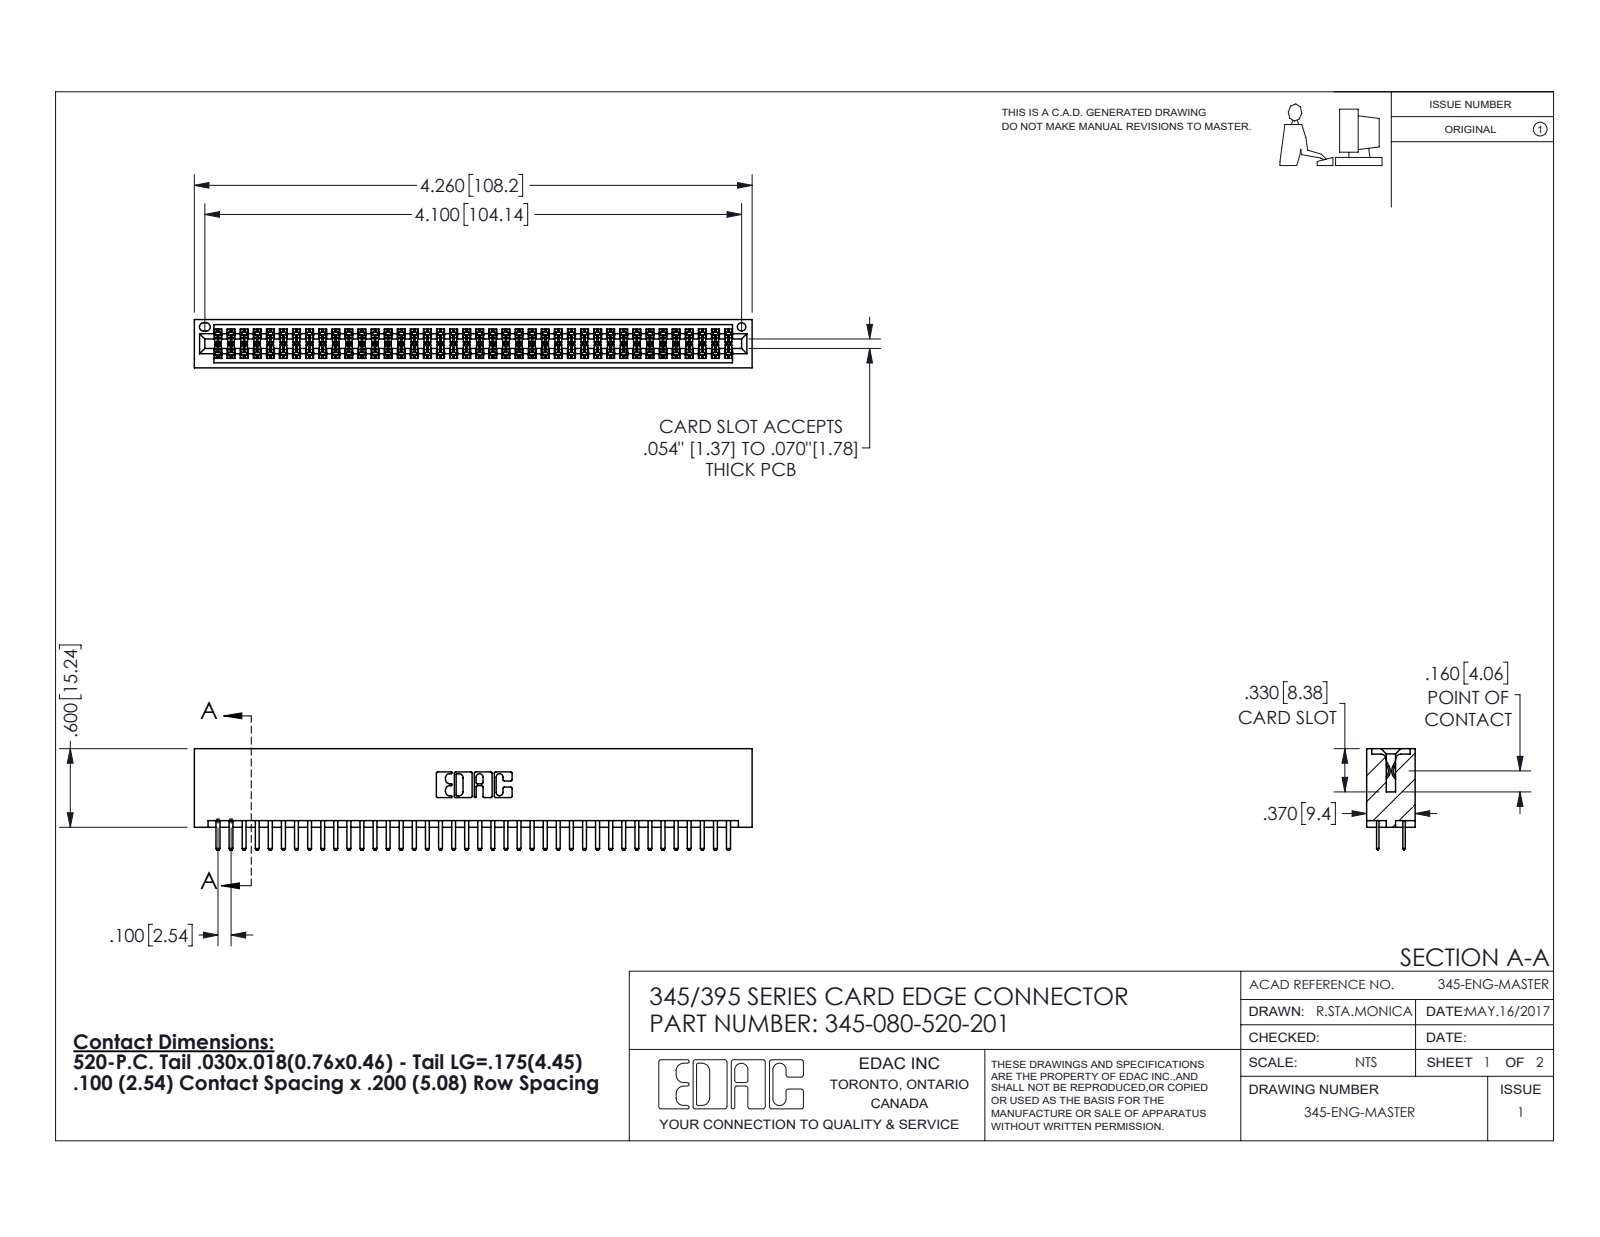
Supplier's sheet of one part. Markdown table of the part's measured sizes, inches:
| quantity | value |
| --- | --- |
| part name | 345-080-520-201; 345-292-001_345-293-120; 345 Part_No Mounting Lugs |
| STEP written by | SolidWorks 2016 (CONFIG_CONTROL_DESIGN) |
| units | inches |
| bodies | 81 solids, 4438 faces (2876 planar, 1562 cylindrical, 0 other) |
| overall size | 4.26 × 0.775 × 0.37 |
| volume | 0.676 in³ |
| surface area | 25.66 in² |
| round holes (diameter × count) | 0.064 × 1 |
| partial cylindrical surfaces (radius × count) | 0.006 × 120, 0.01 × 84, 0.01 × 22, 0.007 × 6, 0.031 × 6, 0.026 × 3, 0.014 × 2, 0.019 × 2 |
| main face-to-face distances | 0.298, 0.072, 0.2, 0.37, 0.098, 0.272, 0.025, 0.225, 0.022, 0.072 |
